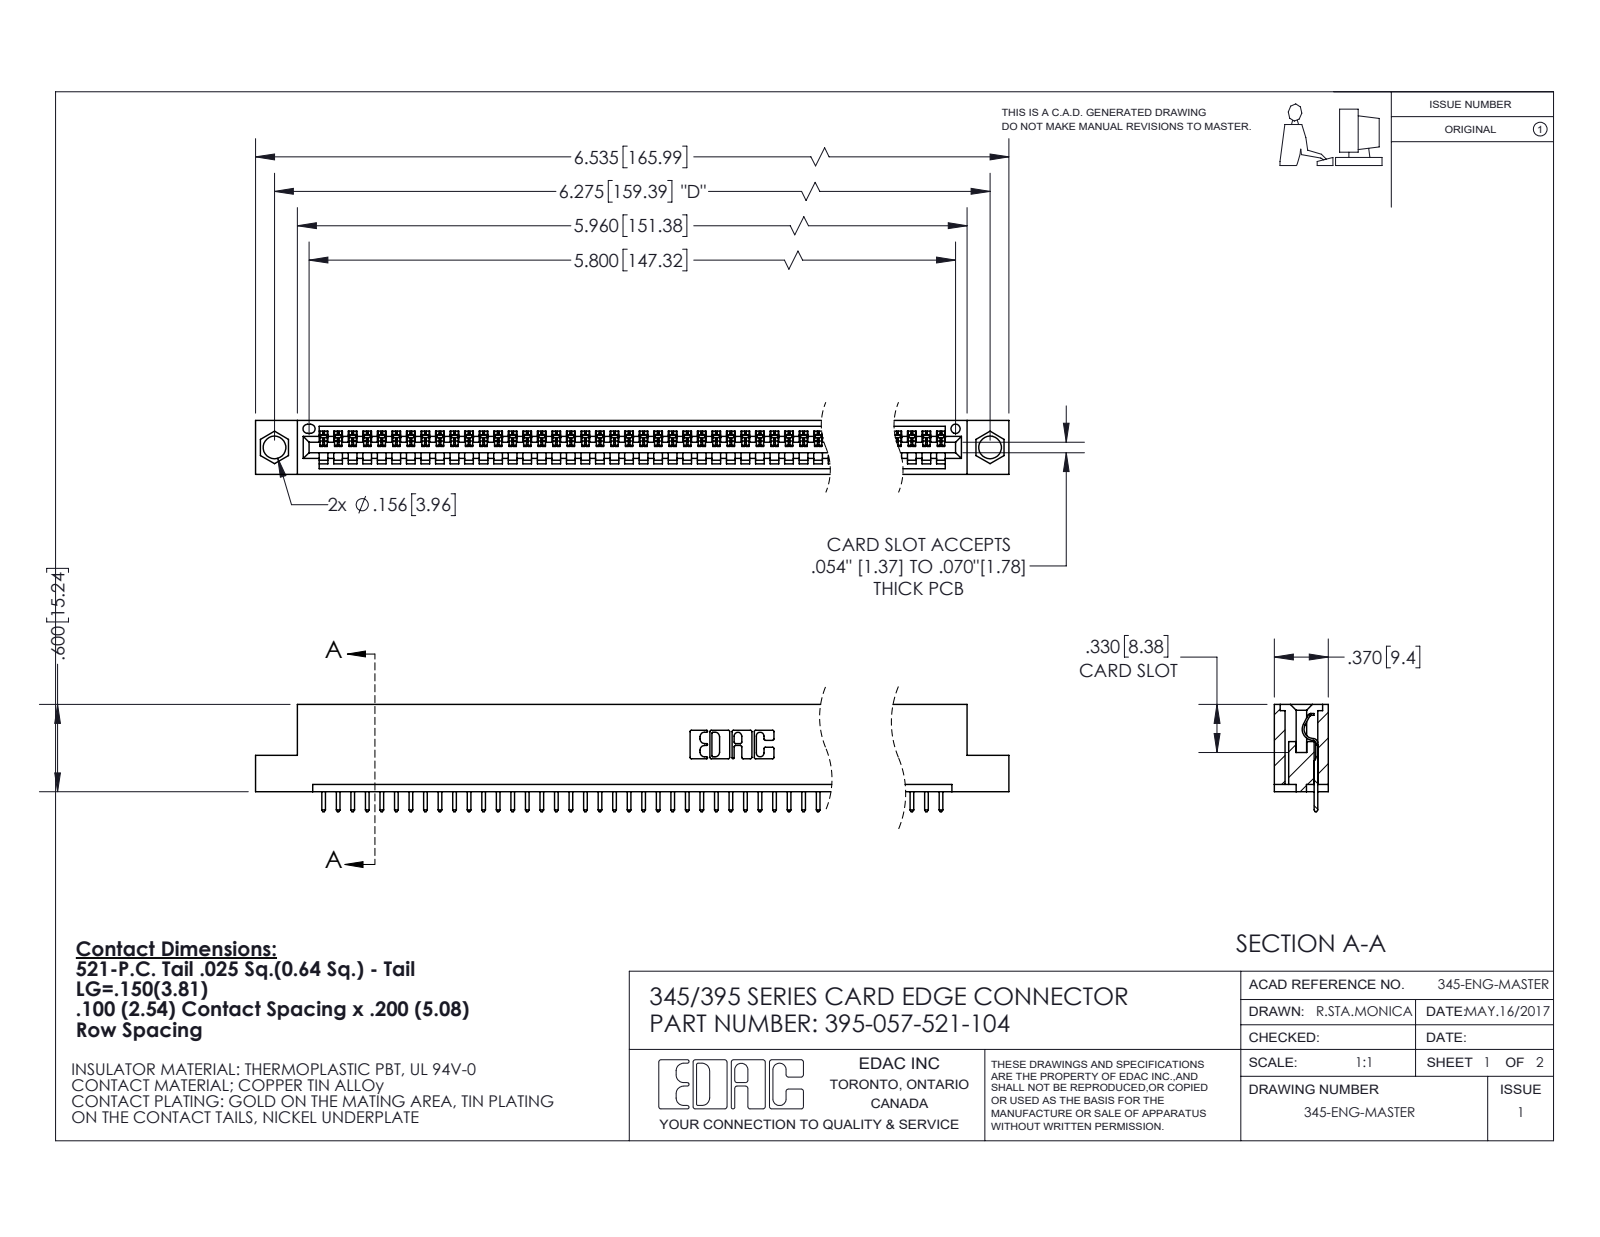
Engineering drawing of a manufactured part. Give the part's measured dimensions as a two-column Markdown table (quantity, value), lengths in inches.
| quantity | value |
| --- | --- |
| part name | 395-057-521-104; 345 Part_Flush Mounting Lugs - 0.156 Dia-TI; 345-292-001_345-293-121 |
| STEP written by | SolidWorks 2020 (CONFIG_CONTROL_DESIGN) |
| units | inches |
| bodies | 58 solids, 3446 faces (2374 planar, 1072 cylindrical, 0 other) |
| overall size | 6.535 × 0.737 × 0.37 |
| volume | 0.953 in³ |
| surface area | 31.26 in² |
| round holes (diameter × count) | 0.156 × 2, 0.064 × 1 |
| partial cylindrical surfaces (radius × count) | 0.006 × 114, 0.01 × 114, 0.01 × 22, 0.007 × 6, 0.031 × 6, 0.026 × 3, 0.031 × 2, 0.04 × 2 |
| main face-to-face distances | 0.298, 0.072, 0.37, 0.2, 0.098, 0.272, 0.025, 0.225, 0.149, 0.072 |
| hole center spacings | 0.27, 6.039, 6.275 |
